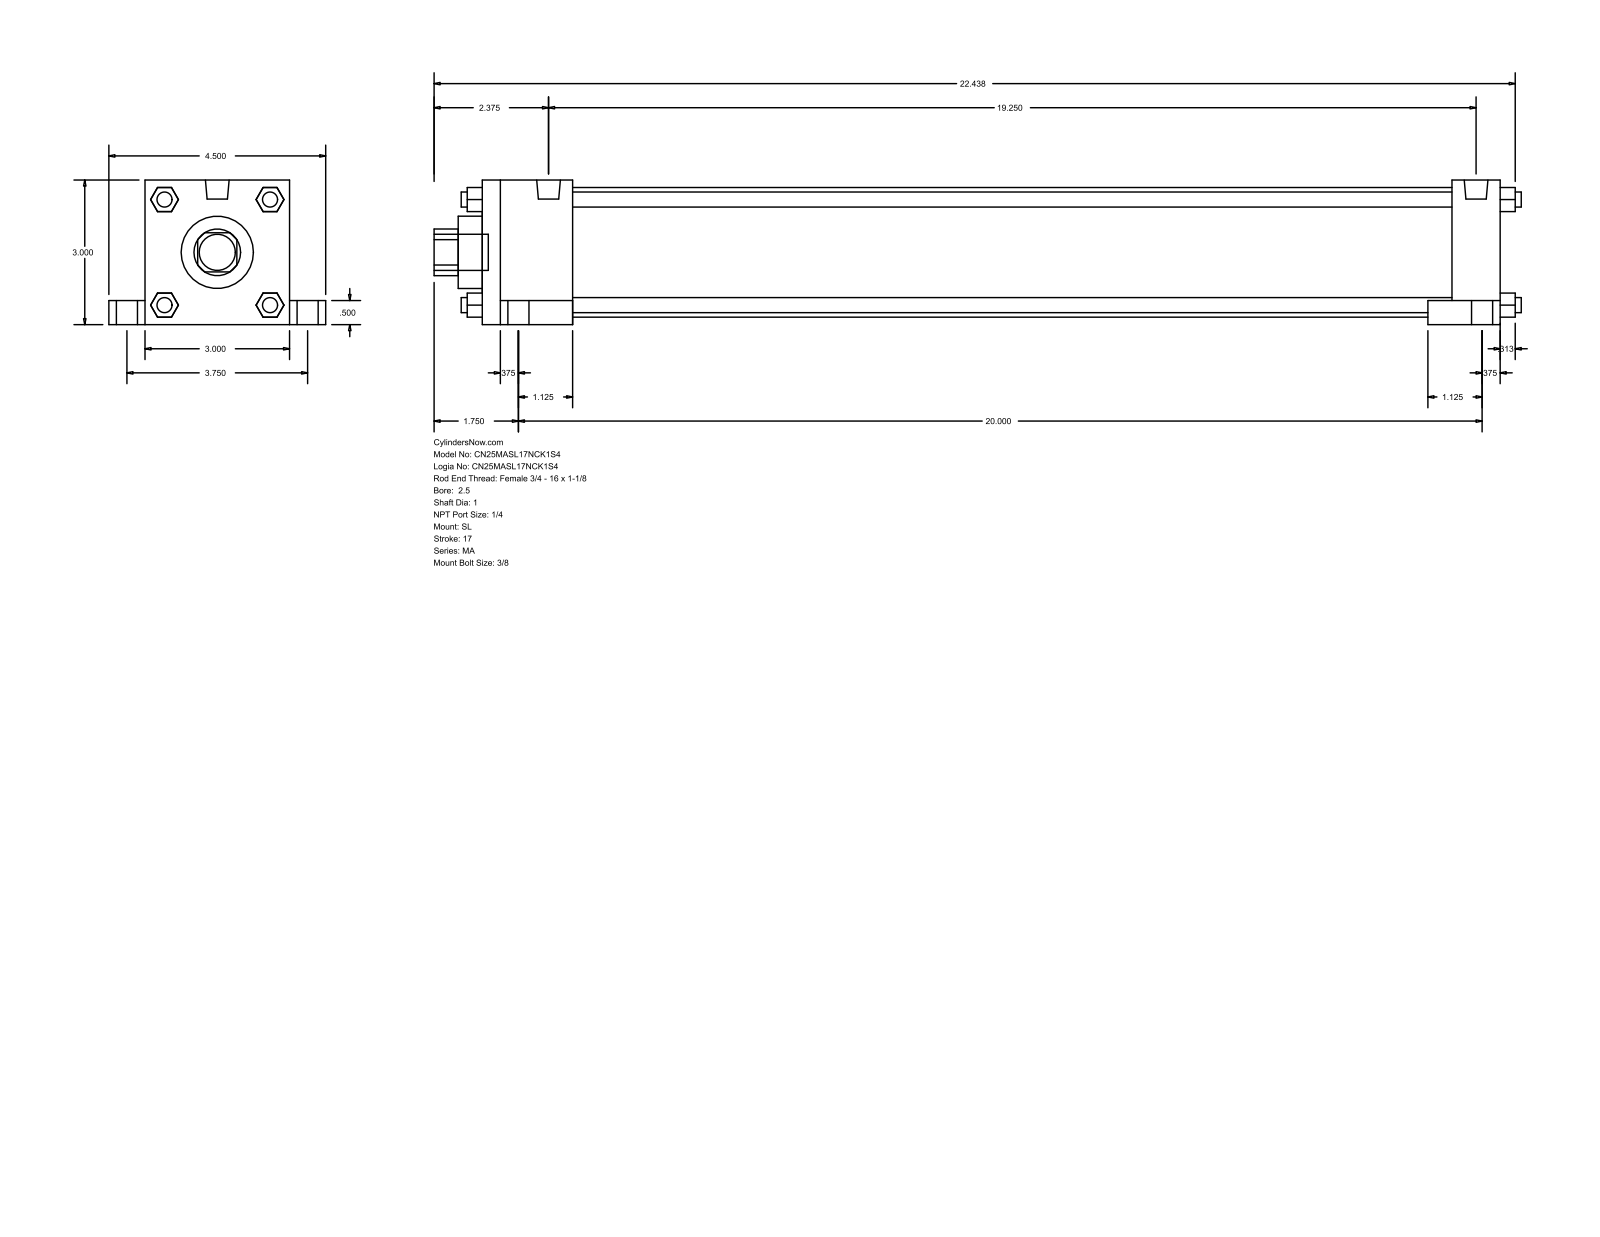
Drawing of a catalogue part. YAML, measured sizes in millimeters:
part_name: "MA_SL__0250_1"
step_written_by: "GSSL Pune (CONFIG_CONTROL_DESIGN)"
units: millimeters
bodies: {solids: 0, faces: 148, planar: 112, cylindrical: 36, other: 0}
overall_size: [573.09, 114.3, 76.2]
round_holes:
  - {diameter: 25.4, count: 1}
  - {diameter: 38.1, count: 1}
  - {diameter: 68.33, count: 1}
round_bosses_or_shafts:
  - {diameter: 7.94, count: 8}
  - {diameter: 17.46, count: 4}
  - {diameter: 11.11, count: 4}
  - {diameter: 12.49, count: 2}
  - {diameter: 19.05, count: 1}
partial_cylinders:
  - {radius: 12.29, count: 1}
face_to_face_distances: [76.2, 536.58, 12.7, 463.55, 25.4, 47.63, 488.95, 511.18, 19.05, 95.25]
